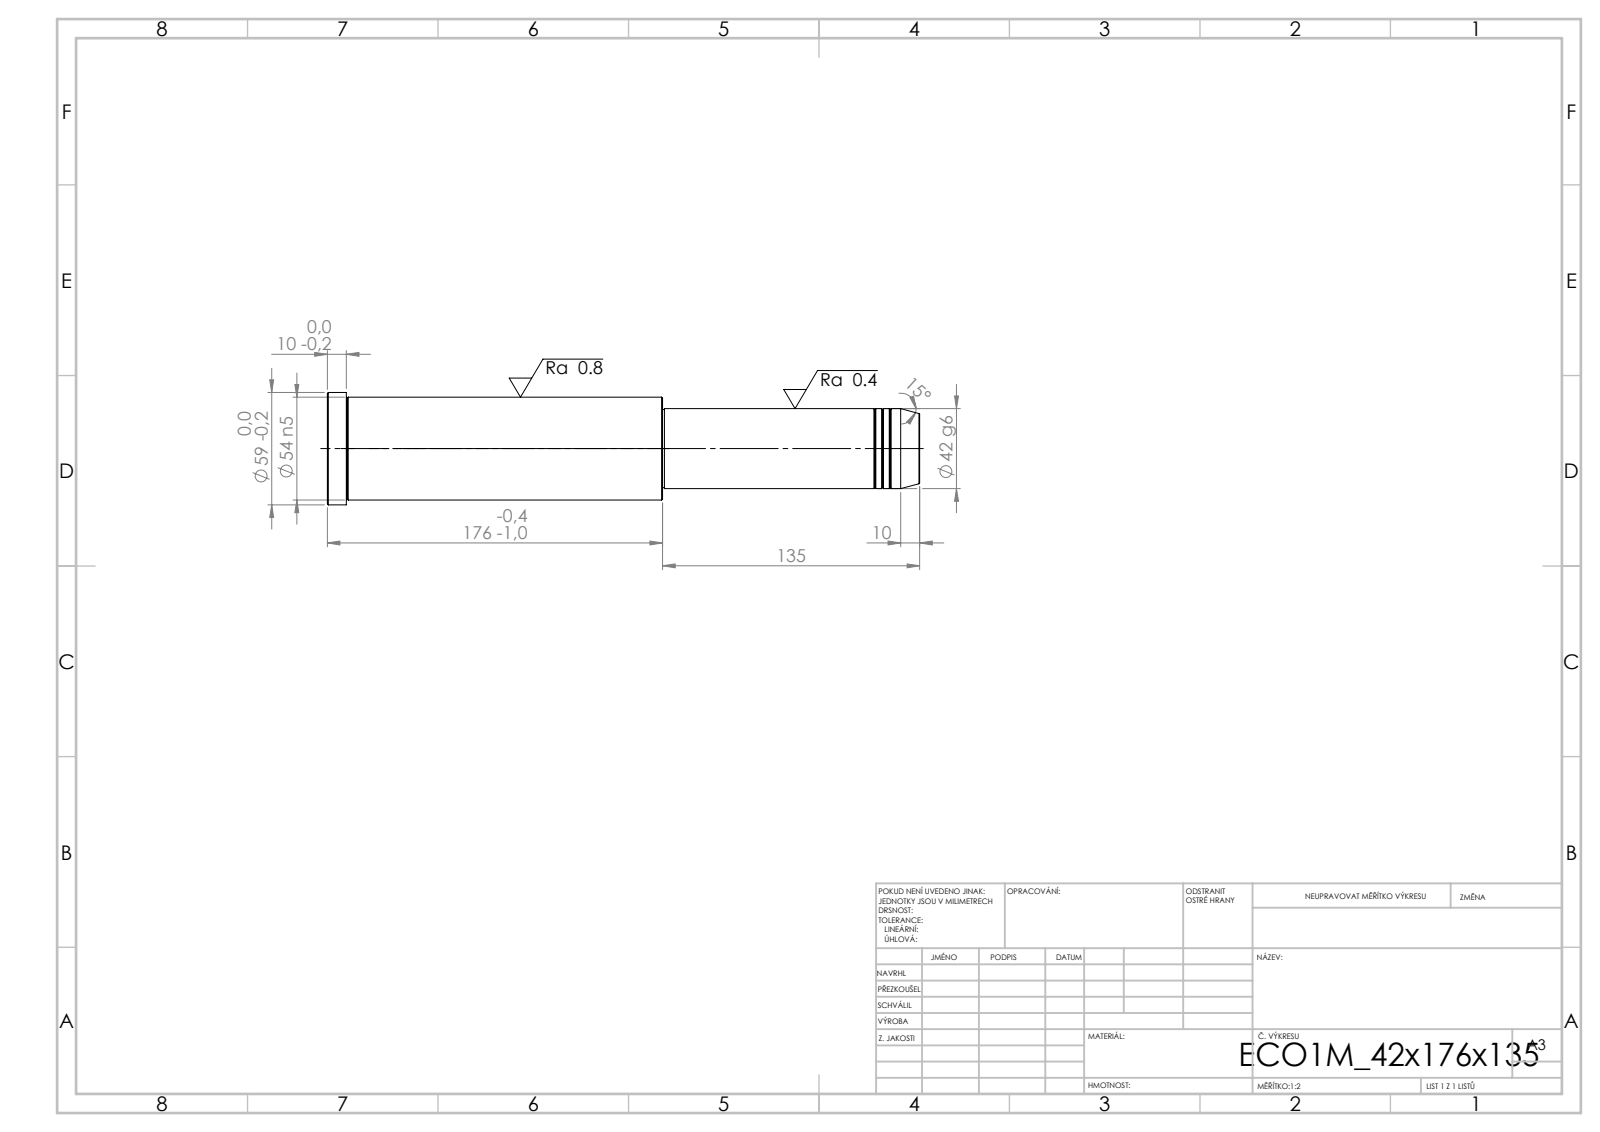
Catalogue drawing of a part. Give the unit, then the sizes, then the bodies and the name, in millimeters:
Units: millimetres
Overall size (bounding box): 311 × 59 × 59
Round bosses / shafts (diameter × count): ⌀59 ×1, ⌀54 ×1, ⌀42 ×1, ⌀41 ×1
Main face-to-face distances: 311, 135, 176, 301, 166, 10, 134, 1, 167, 177
Volume: 592 526 mm³ · Surface area: 53 244 mm²
Bodies: 1 solid, 43 faces (5 planar, 14 cylindrical, 24 other)
STEP written by: SolidWorks 2019 (CONFIG_CONTROL_DESIGN)
